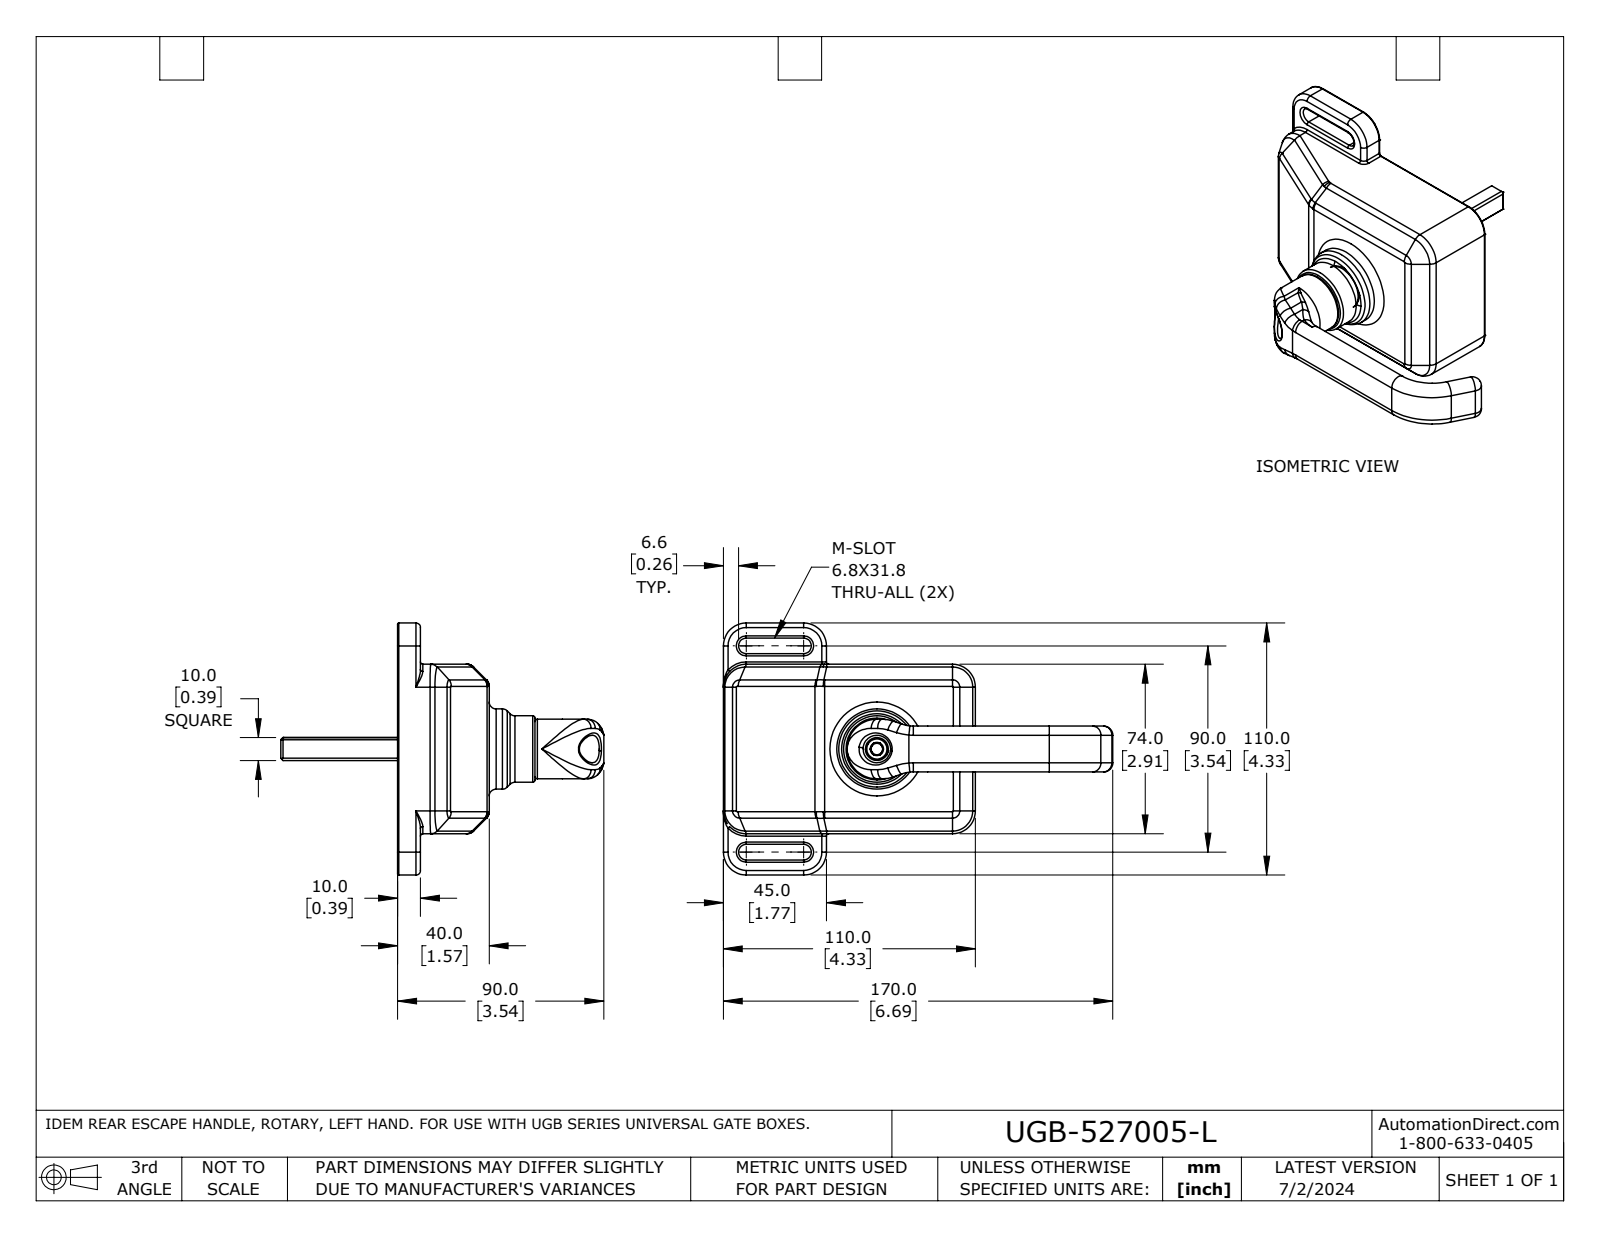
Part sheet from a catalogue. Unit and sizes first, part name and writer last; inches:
Units: inches
Overall size (bounding box): 6.693 × 5.551 × 4.331
Round holes (diameter × count): ⌀0.165 ×4, ⌀0.217 ×4, ⌀0.26 ×1, ⌀0.268 ×1, ⌀0.472 ×1, ⌀0.827 ×1, ⌀0.882 ×1, ⌀0.984 ×1
Round bosses / shafts (diameter × count): ⌀0.335 ×4, ⌀0.197 ×4, ⌀0.173 ×4, ⌀1.378 ×1, ⌀1.142 ×1, ⌀1.024 ×1, ⌀0.787 ×1, ⌀0.394 ×1
Partial cylindrical surfaces — rounded edges, fillets, slot ends (radius × count): R0.039 ×93, R0.02 ×61, R0.157 ×17, R0.394 ×11, R0.079 ×8, R0.134 ×4, R0.177 ×4, R0.236 ×4
Main face-to-face distances: 0.118, 0.079, 2.795, 1.457, 2.677, 1.417, 0.039, 0.315, 0.236, 2.913
Hole centre spacings: 1.679, 2.126, 2.483, 3.543, 4.132
Volume: 8.996 in³ · Surface area: 126.8 in²
Bodies: 10 solids, 783 faces (219 planar, 291 cylindrical, 273 other)
Part name (STEP PRODUCT): UGB-527005-L
STEP written by: SolidWorks 2023 (AUTOMOTIVE_DESIGN)
